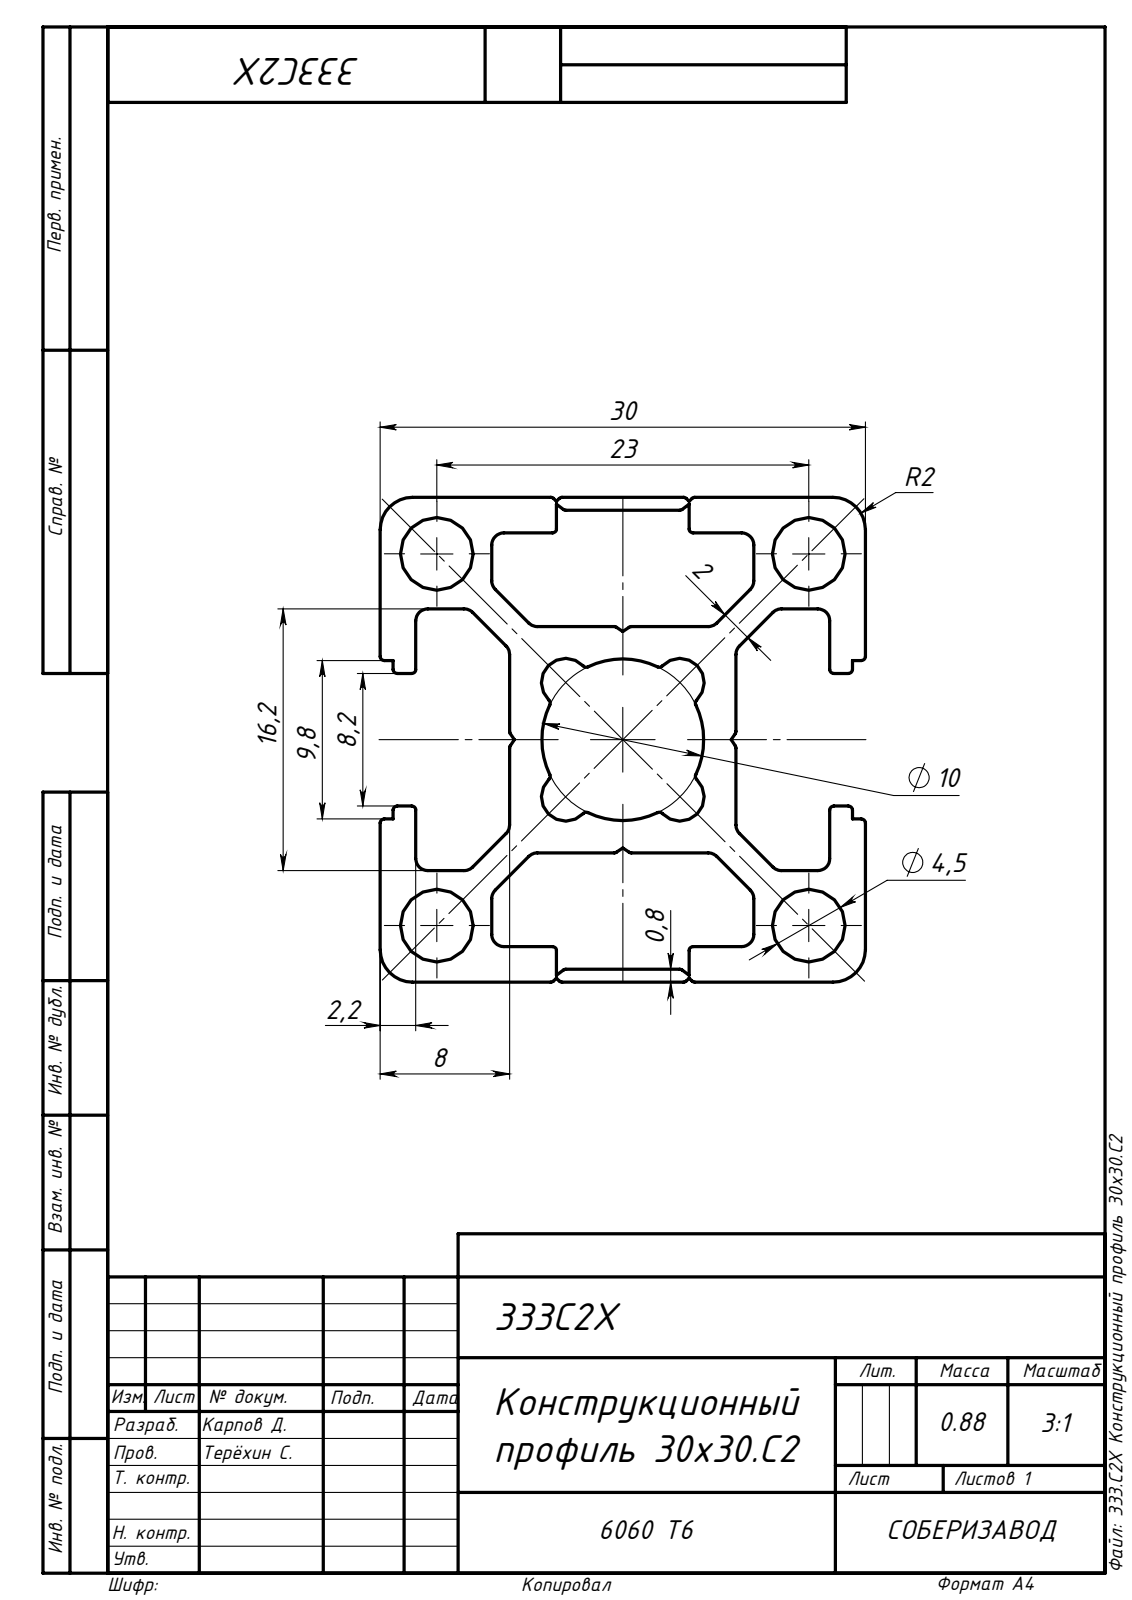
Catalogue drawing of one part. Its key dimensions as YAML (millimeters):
part_name: "333.C2X Конструкционный профиль 30x30.C2"
step_written_by: "SolidWorks 2019 (AUTOMOTIVE_DESIGN)"
units: millimeters
bodies: {solids: 1, faces: 174, planar: 82, cylindrical: 92, other: 0}
overall_size: [1000, 30, 30]
volume: 326925
surface_area: 357698
round_holes:
  - {diameter: 4.5, count: 4}
partial_cylinders:
  - {radius: 0.25, count: 44}
  - {radius: 0.75, count: 24}
  - {radius: 1.5, count: 4}
  - {radius: 2, count: 4}
  - {radius: 5, count: 1}
face_to_face_distances: [30, 8, 22, 5.8, 2.2, 27.8, 19.8, 14, 0.8, 6.9]
hole_center_spacings: [23, 32.53]
